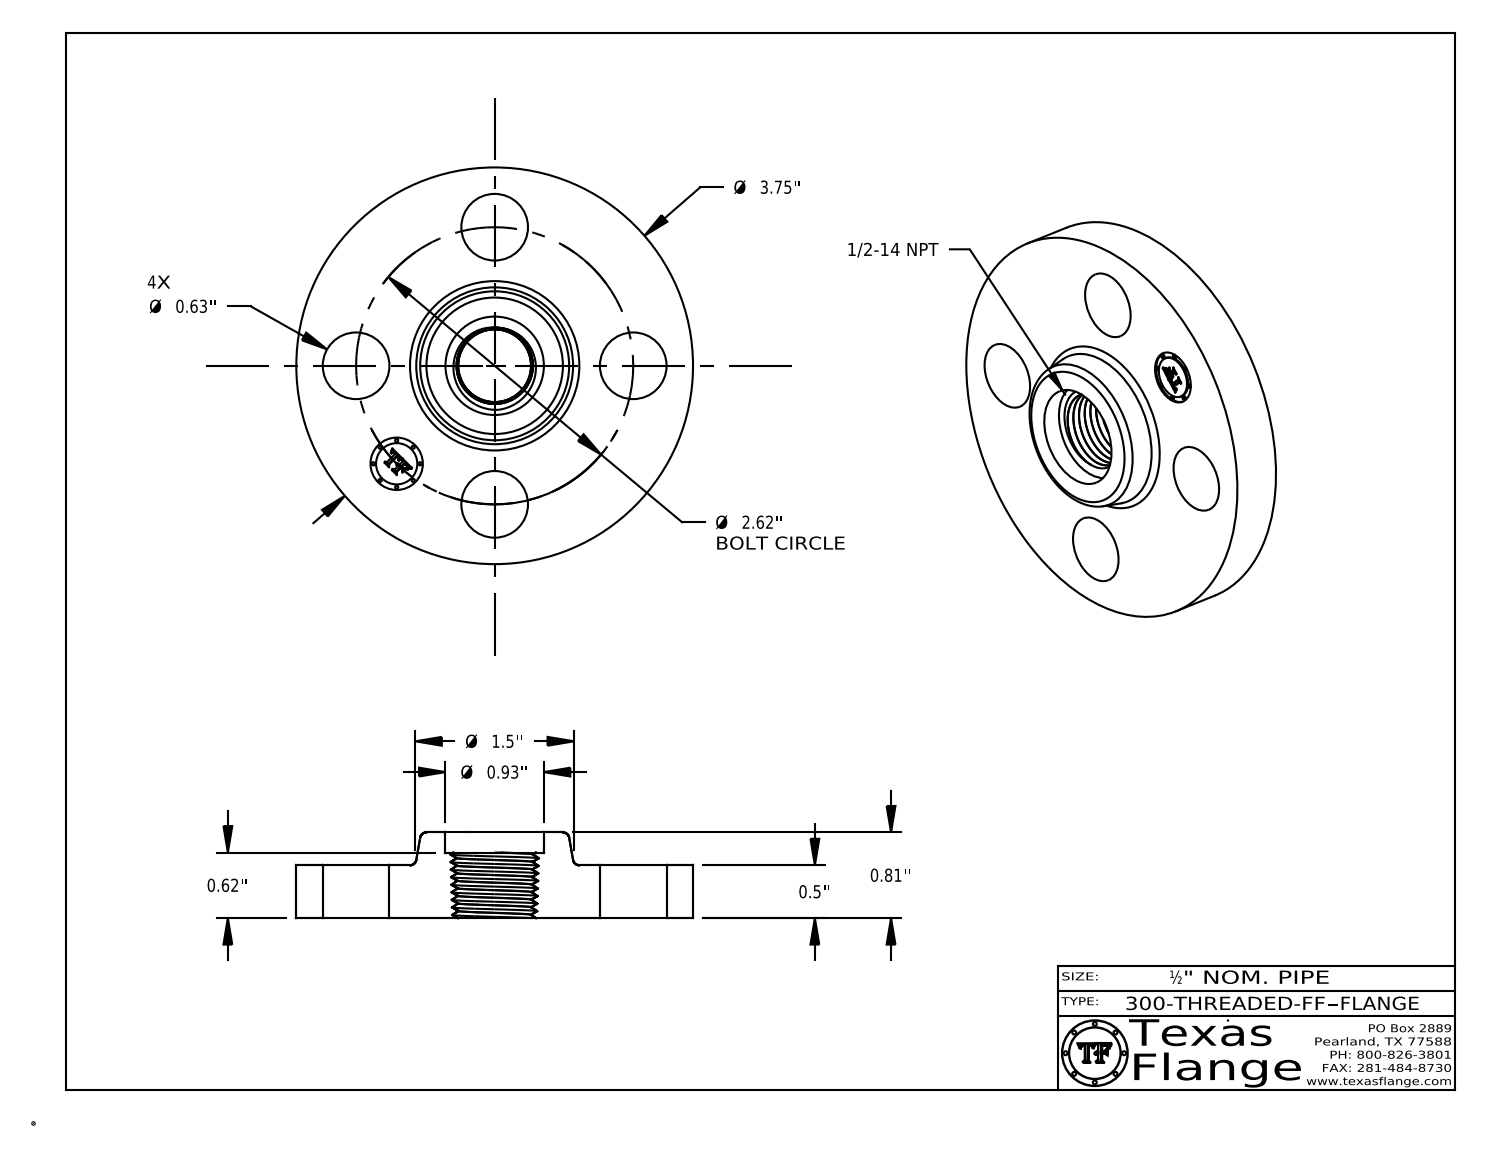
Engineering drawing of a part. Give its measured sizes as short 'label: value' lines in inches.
name: 300-THREADED-FF
written by: CATIA V5 STEP AP214 (AUTOMOTIVE_DESIGN)
unit: in
bodies: 1 solid, 500 faces (369 planar, 32 cylindrical, 99 other)
size: 3.75 × 3.75 × 0.81
volume: 4.997 in³; area: 32.98 in²
holes: 4× ⌀0.63, 1× ⌀0.495, 1× ⌀0.93
bosses: 8× ⌀0.03, 1× ⌀3.75, 1× ⌀0.39
face distances: 0.5, 0.81, 0.31, 0.62, 0.12, 0.19, 0.485, 0.015, 0.135, 0.325
hole spacings: 1.31, 1.852, 1.003, 2.42, 2.62, 1.31
